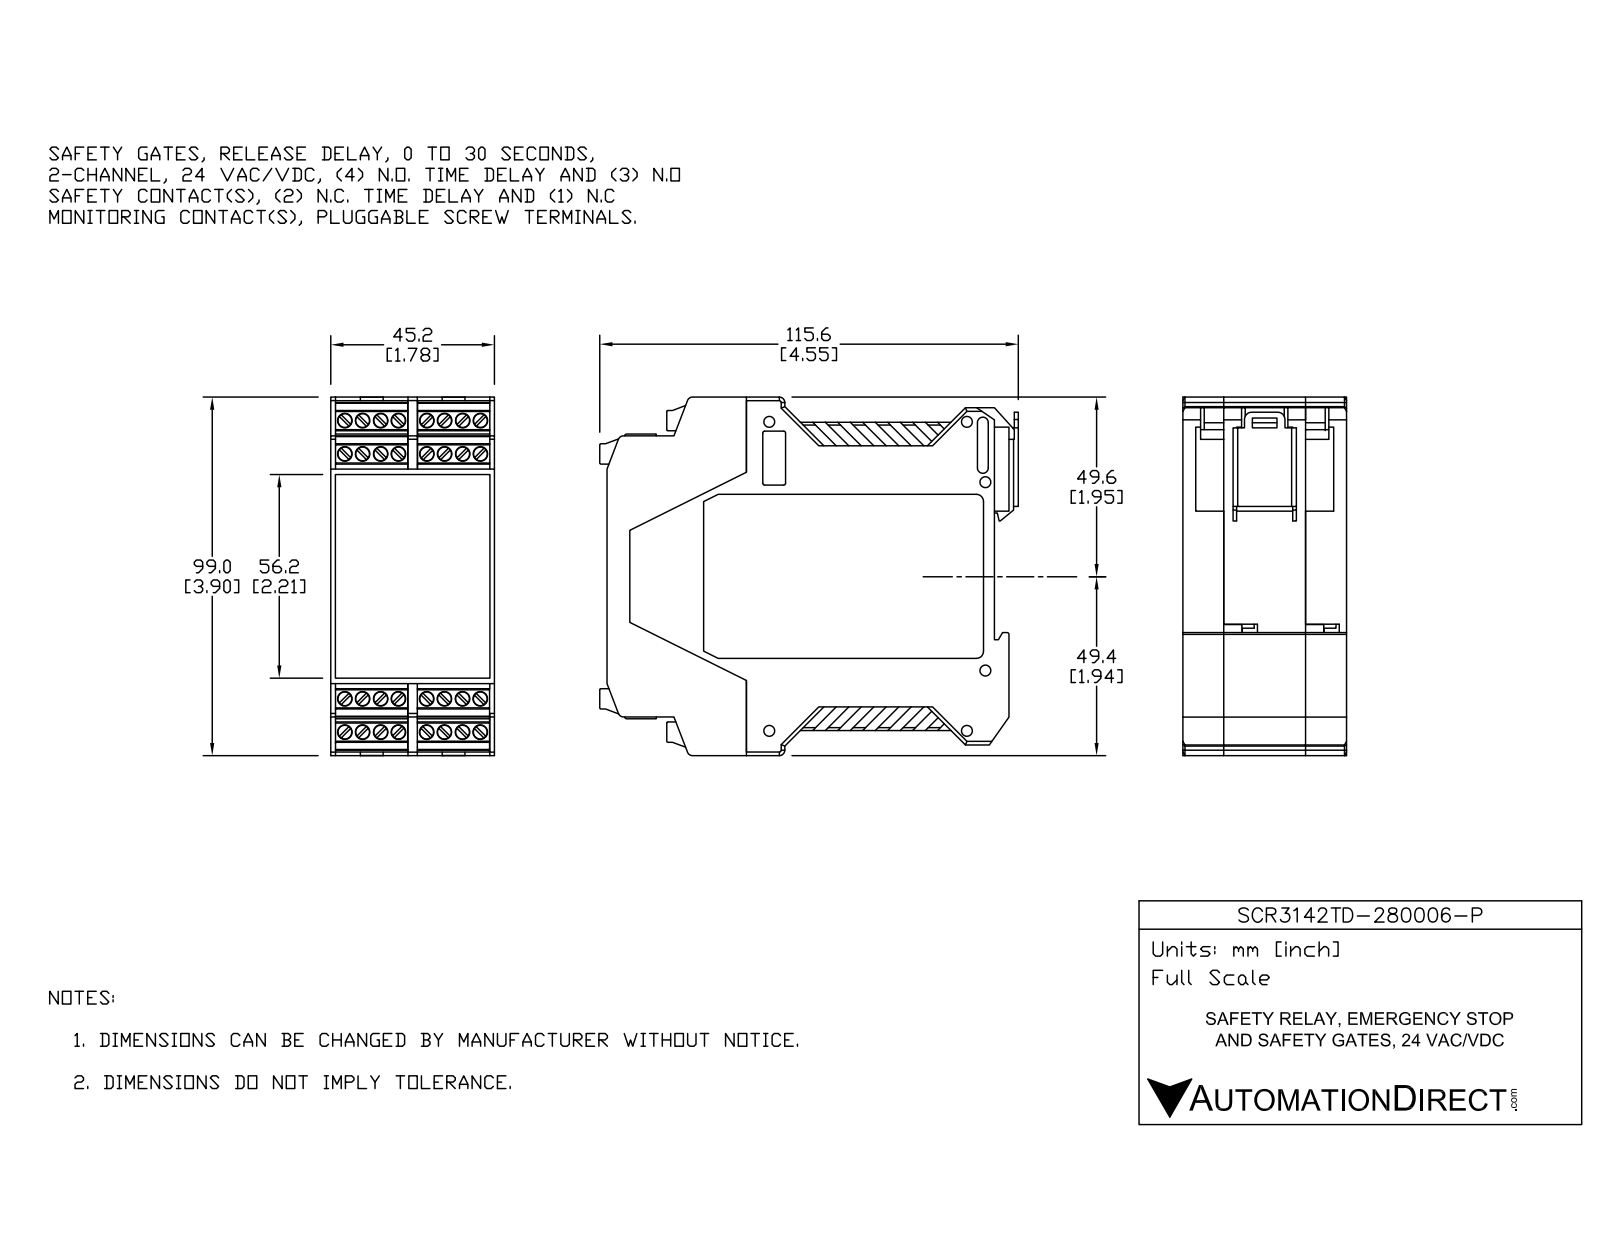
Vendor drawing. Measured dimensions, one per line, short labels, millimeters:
name: 280-Viper-44-P (STEP format)
written by: SolidWorks 2015 (CONFIG_CONTROL_DESIGN)
unit: mm
bodies: 25 solids, 4331 faces (3489 planar, 774 cylindrical, 68 other)
size: 115.6 × 99 × 45.2
volume: 110 467 mm³; area: 121 836 mm²
holes: 32× ⌀4, 8× ⌀3, 2× ⌀2
bosses: 32× ⌀3.8, 16× ⌀2.8, 16× ⌀1.4
rounds: 154× R0.2, 44× R1.2, 21× R0.5, 20× R0.3, 16× R2.92, 12× R0.25, 10× R1.5, 4× R2
face distances: 43.7, 1.5, 1.3, 45, 43.5, 10, 42.2, 45.2, 22.6, 43.9
hole spacings: 9.9, 76.96, 4.9, 9.2, 10.42, 13.51, 76.8, 77.44
